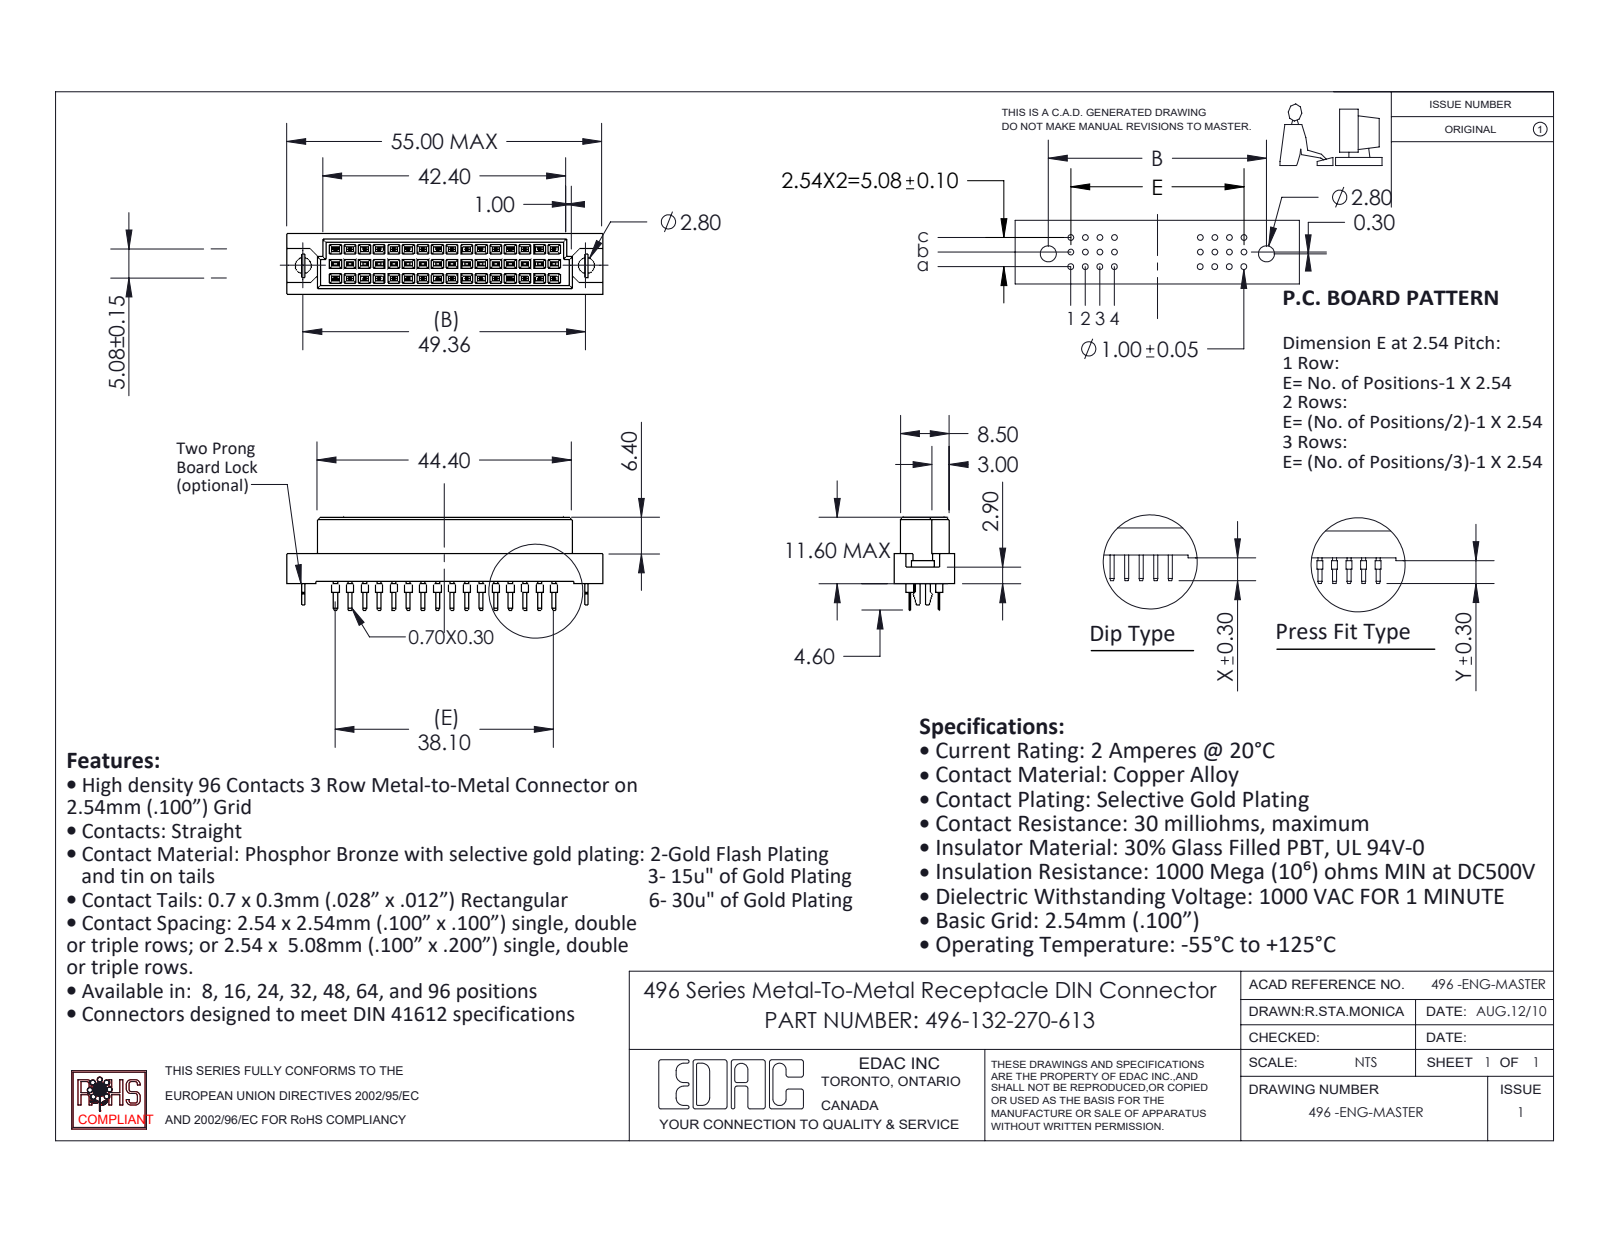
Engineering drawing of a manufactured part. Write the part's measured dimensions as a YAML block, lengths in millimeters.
part_name: "496-290_70; 496-132-270-613; 496 Bore-lock; 496 Part_48"
step_written_by: "SolidWorks 2020 (CONFIG_CONTROL_DESIGN)"
units: millimeters
bodies: {solids: 35, faces: 1278, planar: 1208, cylindrical: 70, other: 0}
overall_size: [55, 16.2, 10.6]
volume: 4699
surface_area: 4992
round_holes:
  - {diameter: 2.8, count: 2}
round_bosses_or_shafts:
  - {diameter: 1, count: 32}
partial_cylinders:
  - {radius: 0.53, count: 1}
face_to_face_distances: [2.54, 5.08, 1.05, 9.55, 0.81, 0.56, 0.55, 10.6, 1.56, 1.86]
hole_center_spacings: [49.36]
